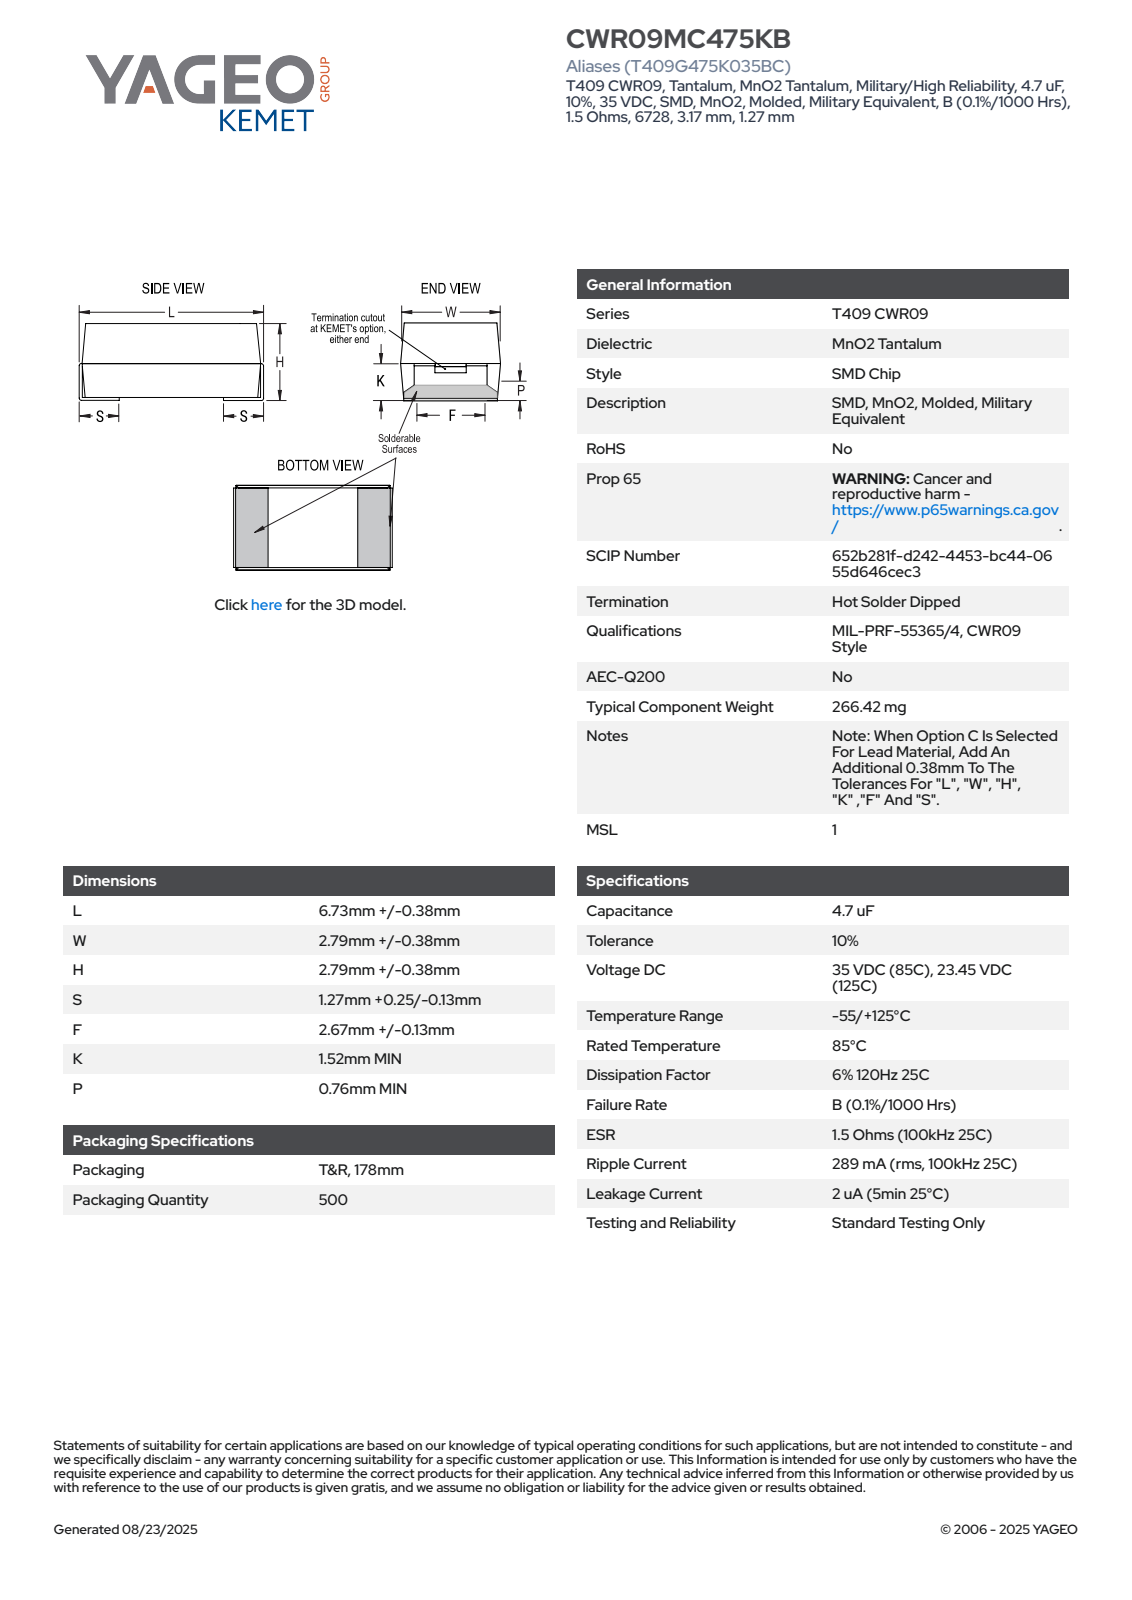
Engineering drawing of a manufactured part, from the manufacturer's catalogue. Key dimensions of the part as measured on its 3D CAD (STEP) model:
Part name (STEP PRODUCT): CTS_TCM3M_6728_L7.11H3.17S1.27F2.8K1.52P0.76W3.17
STEP written by: SolidWorks 2014 (AUTOMOTIVE_DESIGN)
Units: millimetres
Bodies: 4 solids, 85 faces (81 planar, 4 cylindrical, 0 other)
Overall size (bounding box): 7.11 × 3.27 × 3.17
Volume: 63 mm³ · Surface area: 120 mm²
Partial cylindrical surfaces — rounded edges, fillets, slot ends (radius × count): R0.1 ×4
Main face-to-face distances: 3.17, 7.01, 3.27, 6.91, 7.11, 1.27, 5.84, 1.17, 5.74, 2.79
